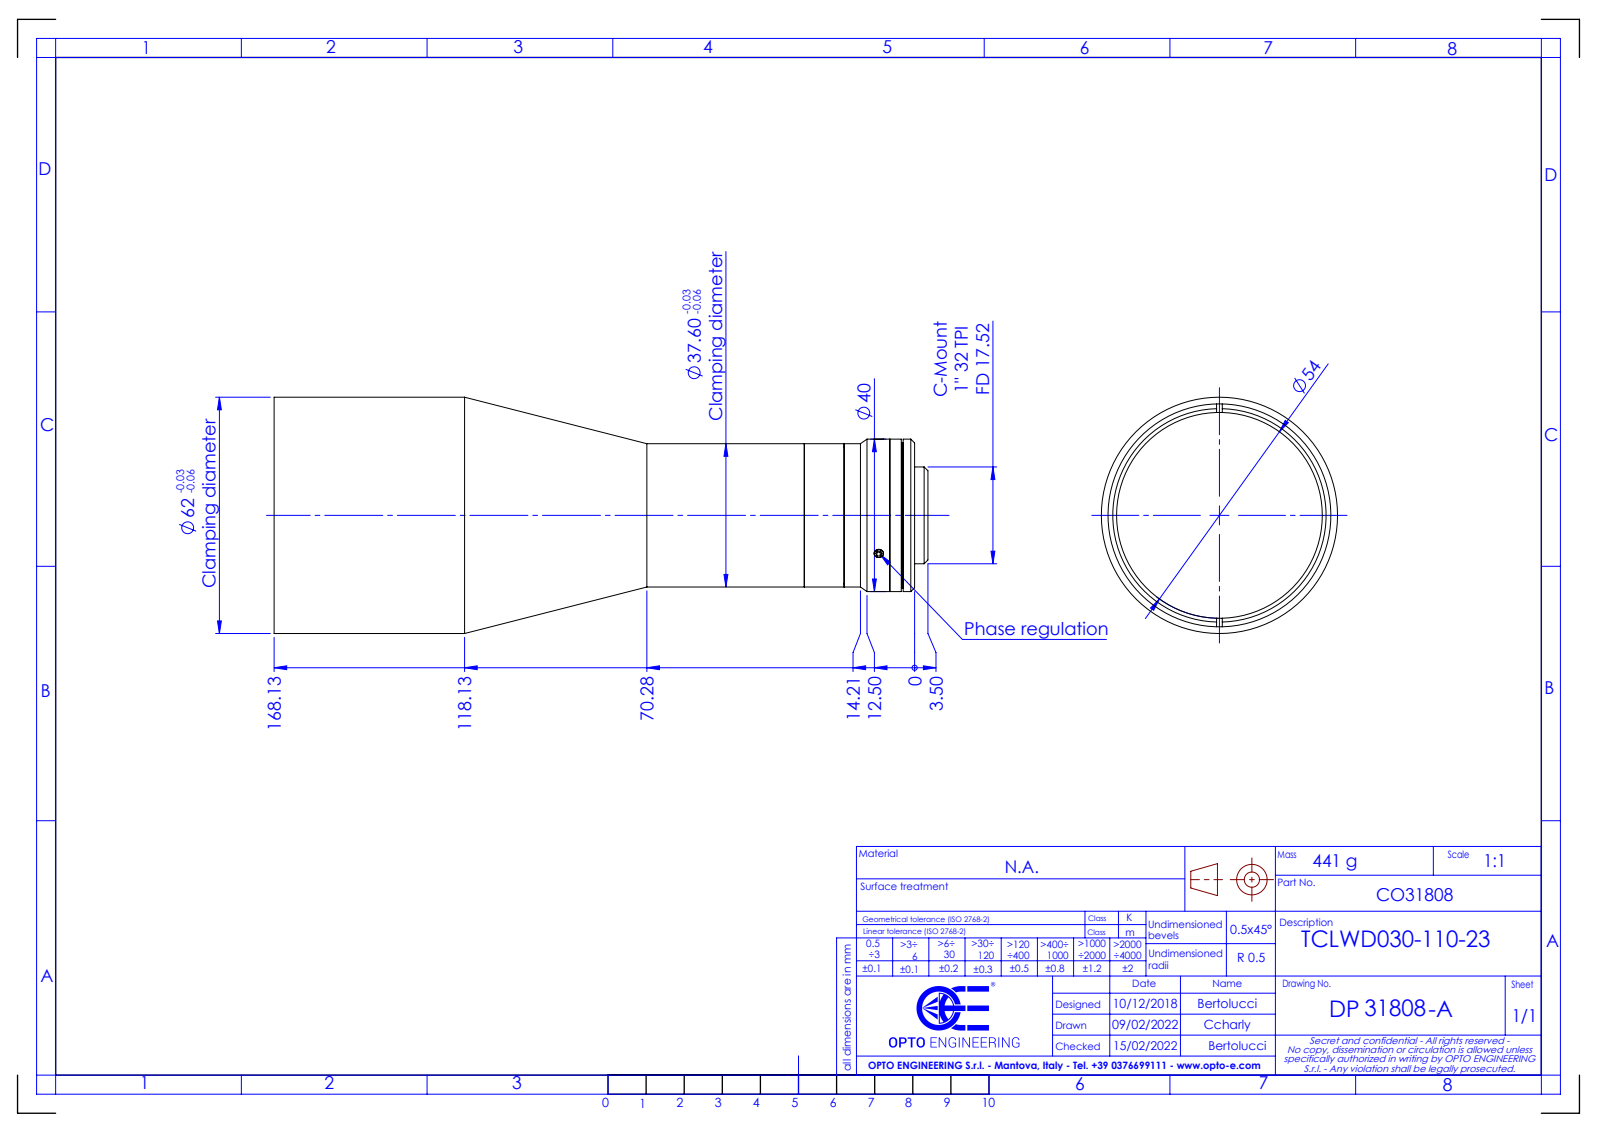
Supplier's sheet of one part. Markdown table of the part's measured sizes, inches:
| quantity | value |
| --- | --- |
| part name | DP31808-A_TCLWD030-110-23 |
| STEP written by | SolidWorks 2021 (CONFIG_CONTROL_DESIGN) |
| units | inches |
| bodies | 0 solids, 82 faces (39 planar, 24 cylindrical, 19 other) |
| overall size | 6.757 × 2.441 × 2.441 |
| round holes (diameter × count) | 0.886 × 1, 1.004 × 1, 2.126 × 1, 2.303 × 1 |
| round bosses / shafts (diameter × count) | 2.441 × 1, 1.575 × 1, 1.48 × 1, 1 × 1 |
| main face-to-face distances | 0.138, 0.118, 0.02, 0.589, 0.608, 0.726, 0.234, 0.354, 0.374, 0.492 |
